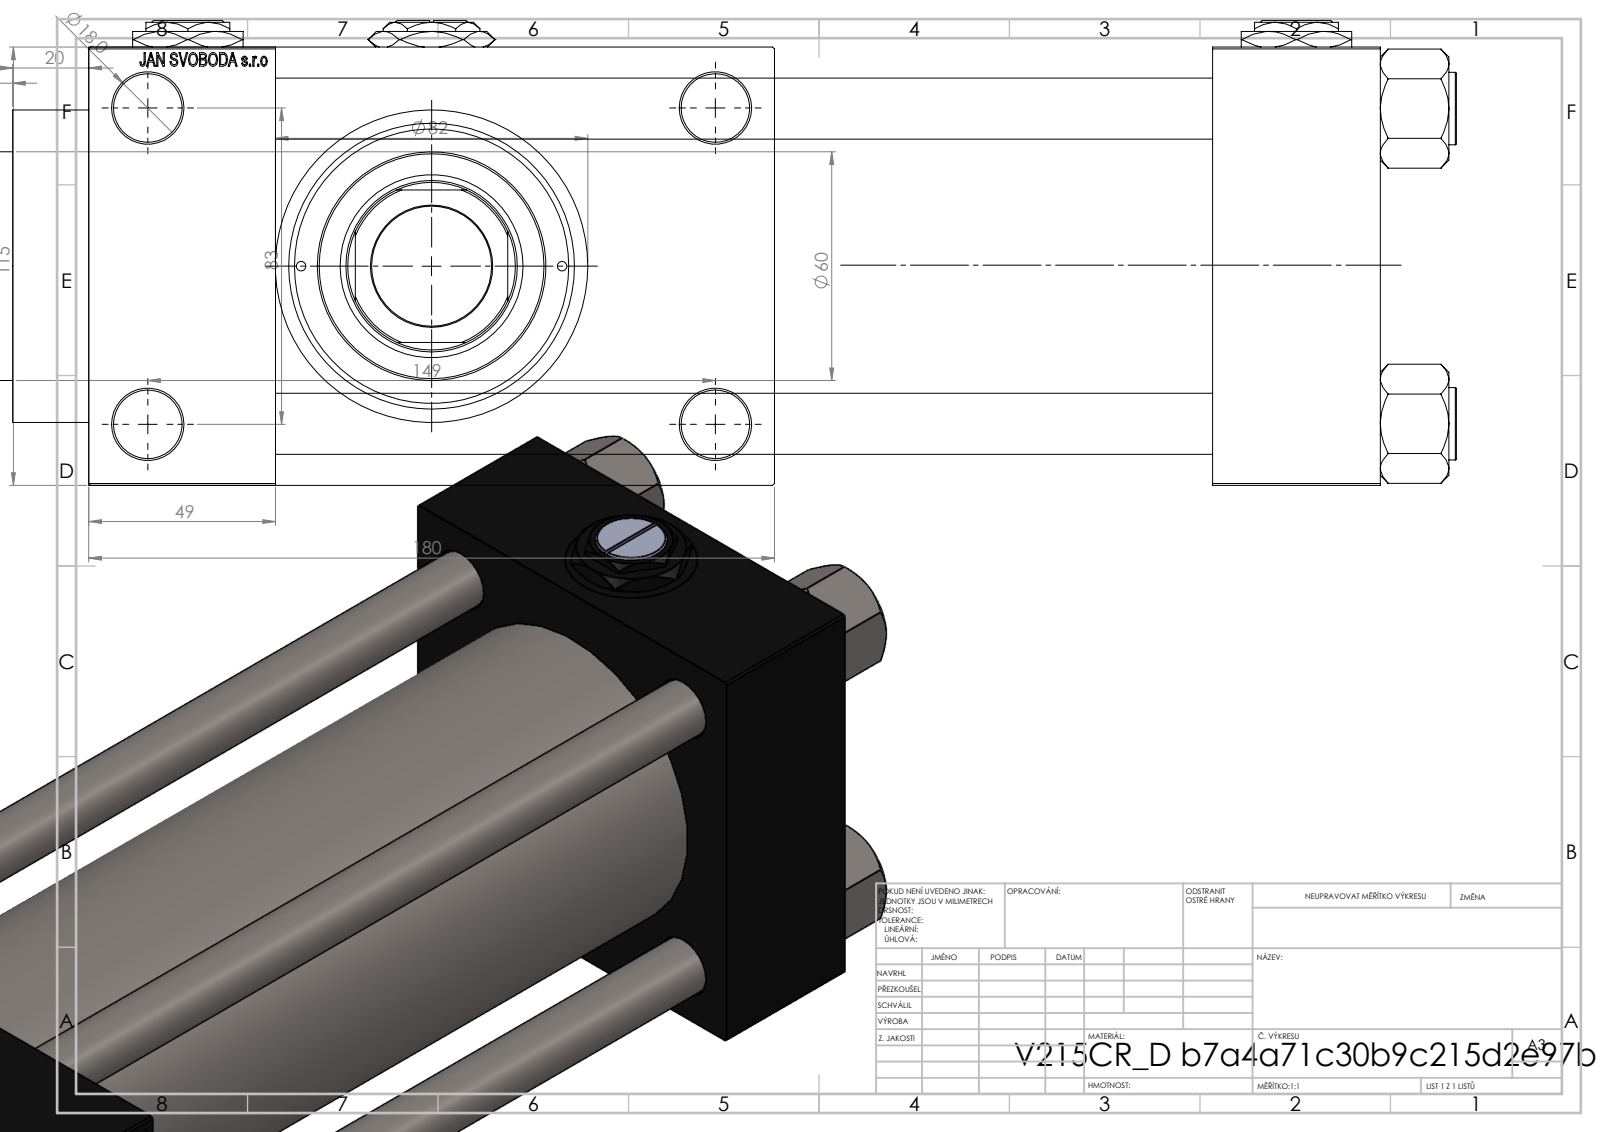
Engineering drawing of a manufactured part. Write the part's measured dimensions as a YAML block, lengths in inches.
part_name: "V215CR_D_TYCINKA; V215_VC_A; NUT_M5_D; Zatka_pro_OIL_PORT (+2 more)"
step_written_by: "SolidWorks 2019 (CONFIG_CONTROL_DESIGN)"
units: inches
bodies: {solids: 13, faces: 1260, planar: 595, cylindrical: 103, other: 562}
overall_size: [16.142, 7.087, 4.803]
volume: 156.3
surface_area: 720.1
round_holes:
  - {diameter: 0.63, count: 4}
  - {diameter: 0.709, count: 4}
  - {diameter: 1.041, count: 4}
  - {diameter: 1.378, count: 4}
  - {diameter: 0.276, count: 3}
  - {diameter: 0.098, count: 2}
  - {diameter: 1.24, count: 1}
  - {diameter: 1.772, count: 1}
  - {diameter: 1.89, count: 1}
  - {diameter: 2.402, count: 1}
  - {diameter: 2.835, count: 1}
  - {diameter: 3.15, count: 1}
round_bosses_or_shafts:
  - {diameter: 0.748, count: 4}
  - {diameter: 3.386, count: 1}
  - {diameter: 3.228, count: 1}
  - {diameter: 2.362, count: 1}
partial_cylinders:
  - {radius: 0.866, count: 1}
face_to_face_distances: [4.528, 9.685, 11.614, 1.929, 1.732, 11.417, 13.346, 1.28, 5.807, 7.087]
hole_center_spacings: [1.305, 1.652, 2.276, 2.302, 3.256, 3.357, 3.393, 3.513]
